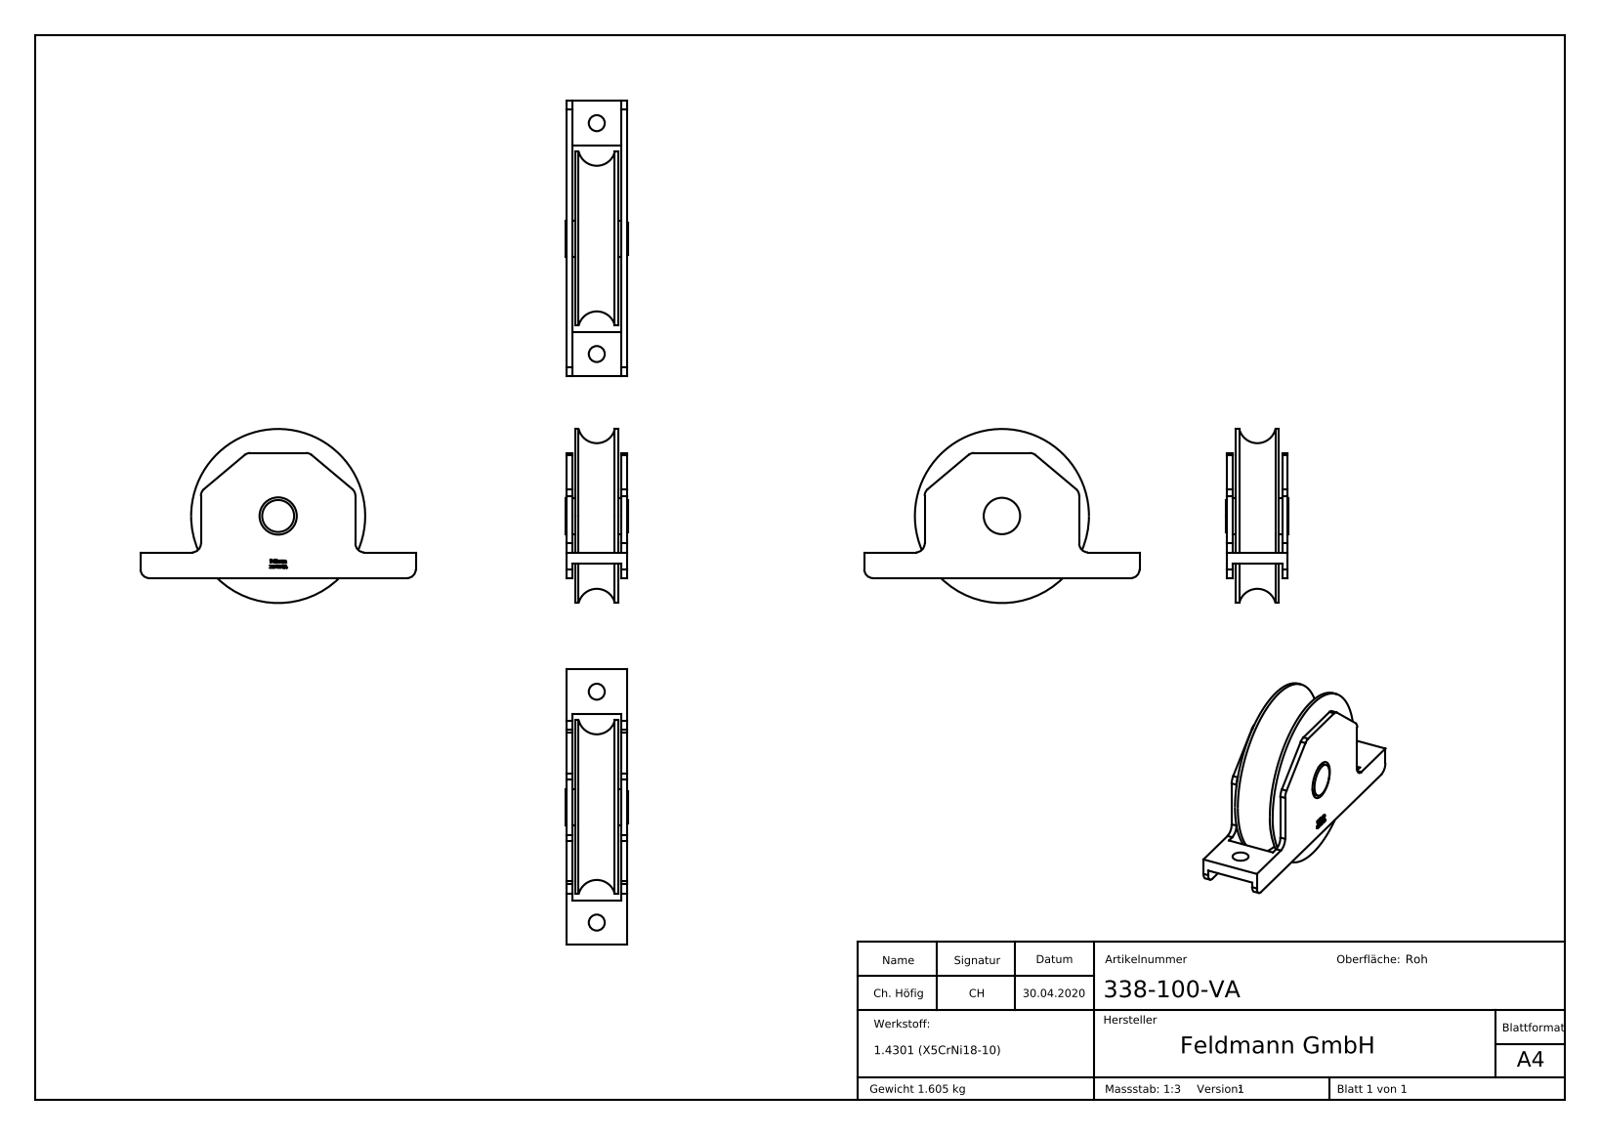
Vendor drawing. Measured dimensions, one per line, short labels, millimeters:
name: 338-100-VA
written by: SolidWorks 2015 (CONFIG_CONTROL_DESIGN)
unit: mm
bodies: 2 solids, 280 faces (143 planar, 23 cylindrical, 114 other)
size: 155 × 88 × 35
volume: 171 963 mm³; area: 53 201 mm²
holes: 2× ⌀9
bosses: 1× ⌀88, 1× ⌀20.5, 1× ⌀18
rounds: 8× R5
face distances: 5, 29, 3, 31, 2, 26, 34, 24, 28, 6.5
hole spacings: 130
